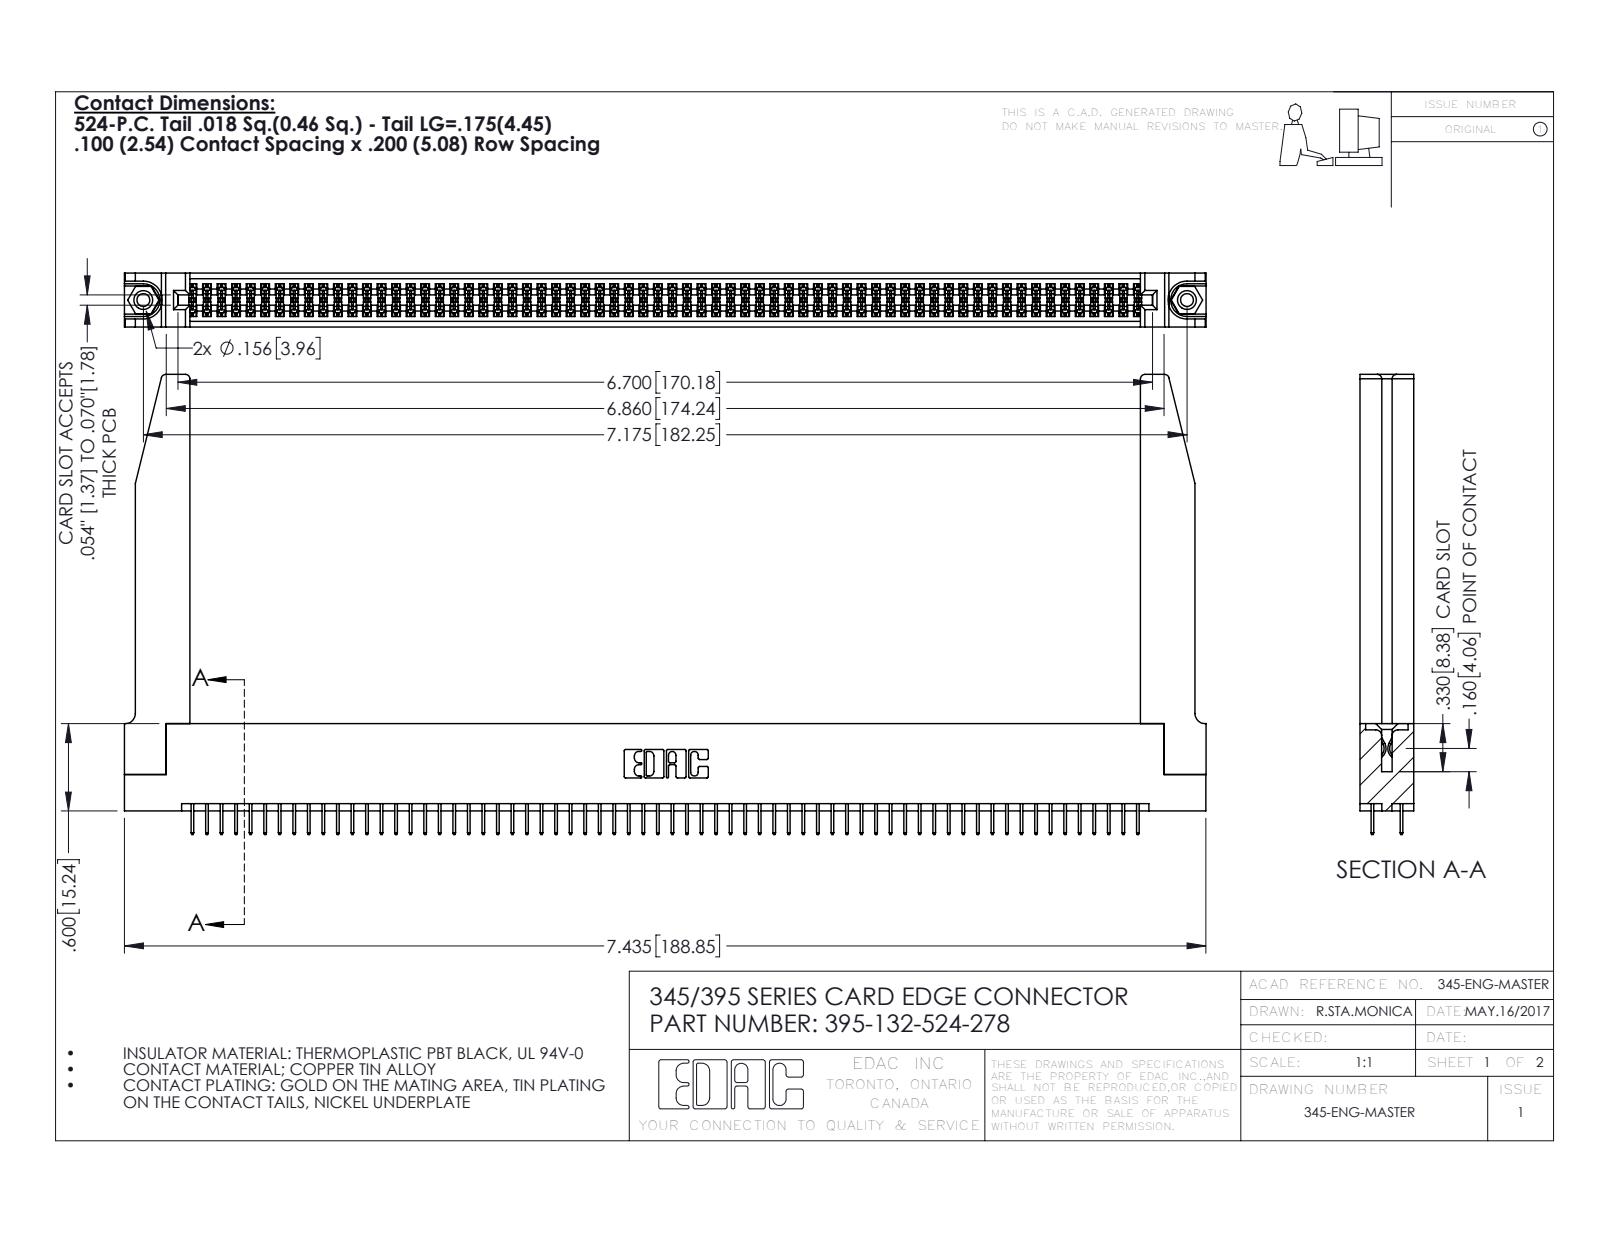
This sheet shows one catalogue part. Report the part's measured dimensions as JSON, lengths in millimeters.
{"part_name": "345-220-078_345-220-078; 345-250-001_345-250-001-102; 345-292-001_345-293-124; 395-132-524-278 (+1 more)", "step_written_by": "SolidWorks 2016 (CONFIG_CONTROL_DESIGN)", "units": "millimeters", "bodies": {"solids": 137, "faces": 7488, "planar": 5370, "cylindrical": 2066, "other": 52}, "overall_size": [188.9, 80.3, 9.4], "volume_mm3": 26140, "surface_area_mm2": 33930, "round_holes": [[2.3, 2], [3.2, 2], [4, 2], [1.6, 1]], "round_bosses_or_shafts": [[3.9, 2]], "partial_cylinders_radius": [[0.2, 198], [0.3, 22], [0.8, 8], [0.2, 6], [0.8, 6], [0.7, 3], [0.4, 2], [0.5, 2]], "face_to_face_distances": [1.8, 7.6, 9.4, 5.1, 2.5, 6.9, 0.6, 5.7, 1.8, 4.4], "hole_center_spacings": [6.9, 176.3, 182.2]}
